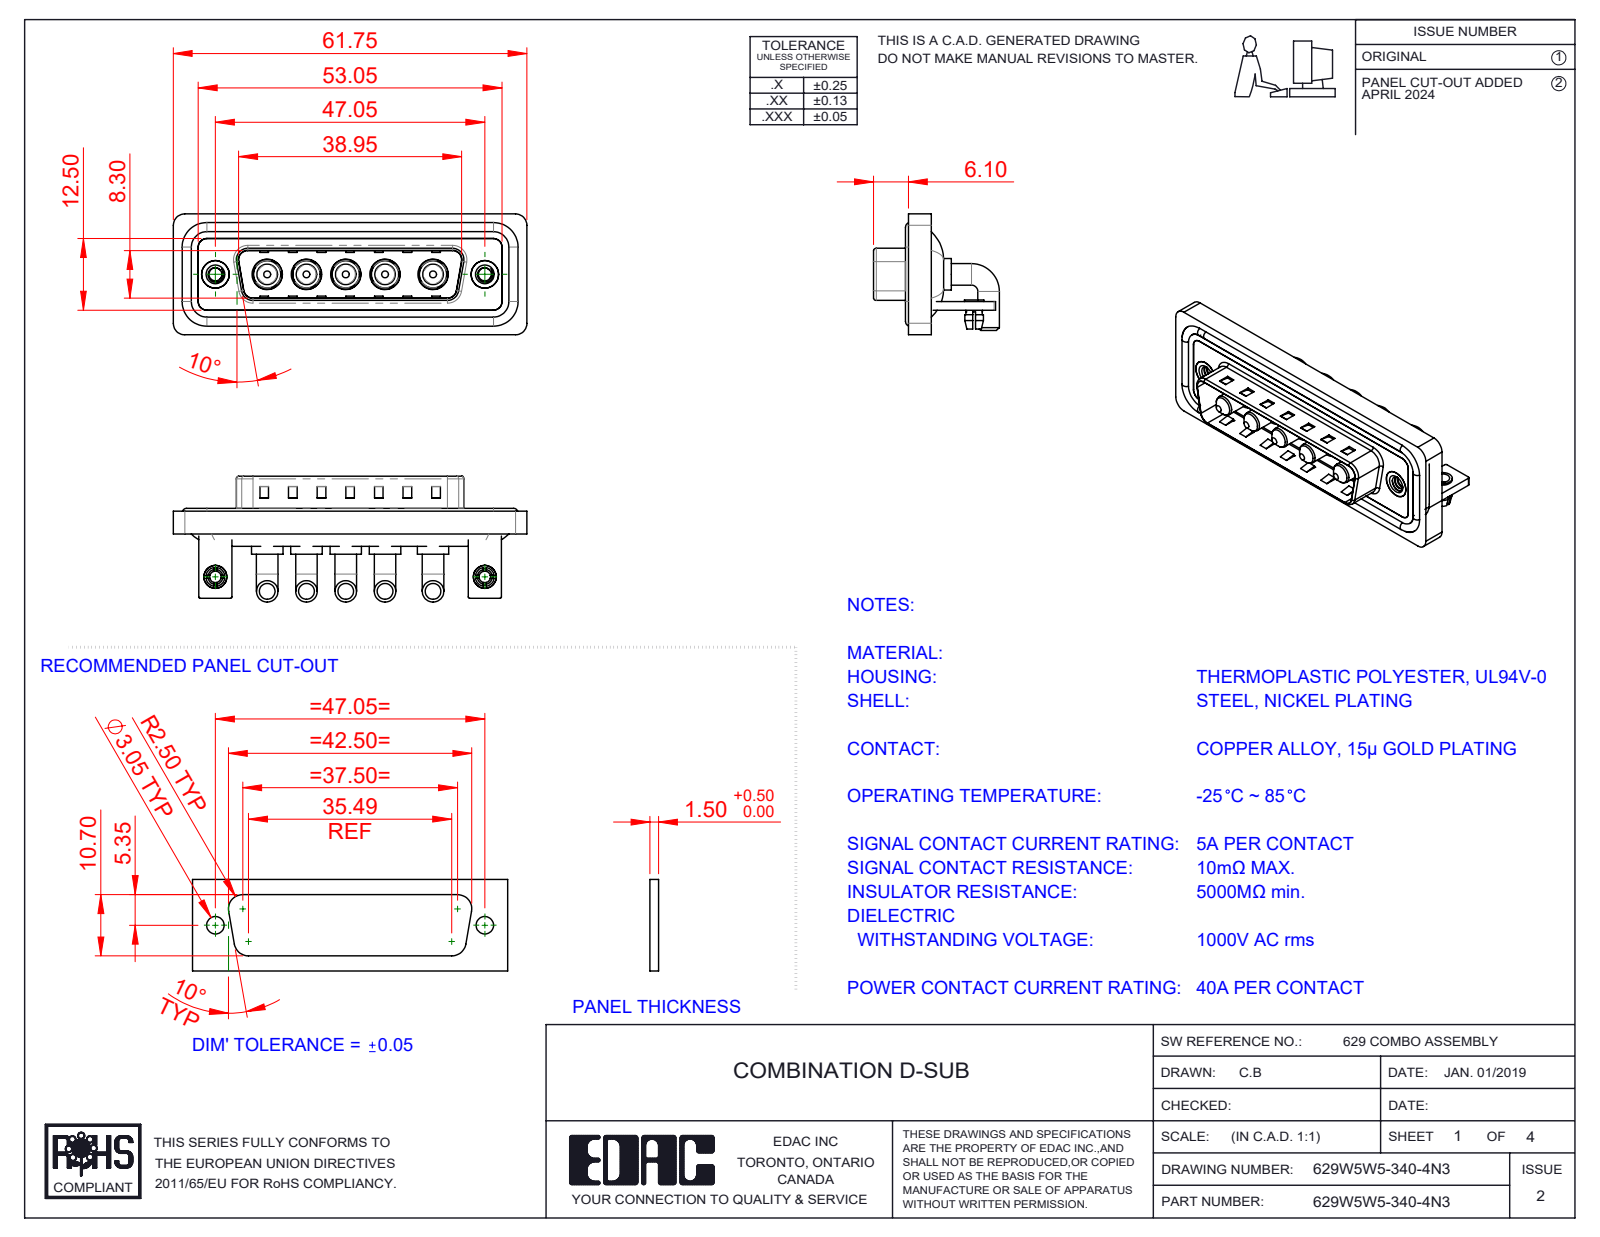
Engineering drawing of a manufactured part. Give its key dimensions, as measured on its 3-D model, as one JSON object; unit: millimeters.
{"part_name": "629Combo Stabilizer Bracket; 629Combo Shell Front_25 Contacts; 629Combo Housing_5W5; 629W5W5-340-4N3 (+5 more)", "step_written_by": "SolidWorks 2023 (CONFIG_CONTROL_DESIGN)", "units": "millimeters", "bodies": {"solids": 21, "faces": 830, "planar": 327, "cylindrical": 343, "other": 160}, "overall_size": [61.75, 21.98, 21.1], "volume_mm3": 8480, "surface_area_mm2": 13289, "round_holes": [[4.85, 5], [5.3, 5], [2, 2], [2.26, 2], [2.5, 2], [3.2, 2], [4, 2], [4.8, 2], [5, 2]], "round_bosses_or_shafts": [[3.75, 10], [5.5, 5], [5.2, 5], [4.75, 5], [3.6, 5], [1.6, 4], [4.9, 2], [4, 2]], "partial_cylinders_radius": [[2, 19], [1.5, 18], [0.25, 16], [0.5, 9], [1.6, 8], [2.1, 5], [0.6, 4], [0.65, 4]], "face_to_face_distances": [0.4, 1.5, 2.9, 0.8, 2.1, 1.1, 3.7, 4.5, 4.1, 1.2], "hole_center_spacings": [6.86, 13.73, 47.05, 6.85, 6.87, 8.37, 8.38, 9.04]}
